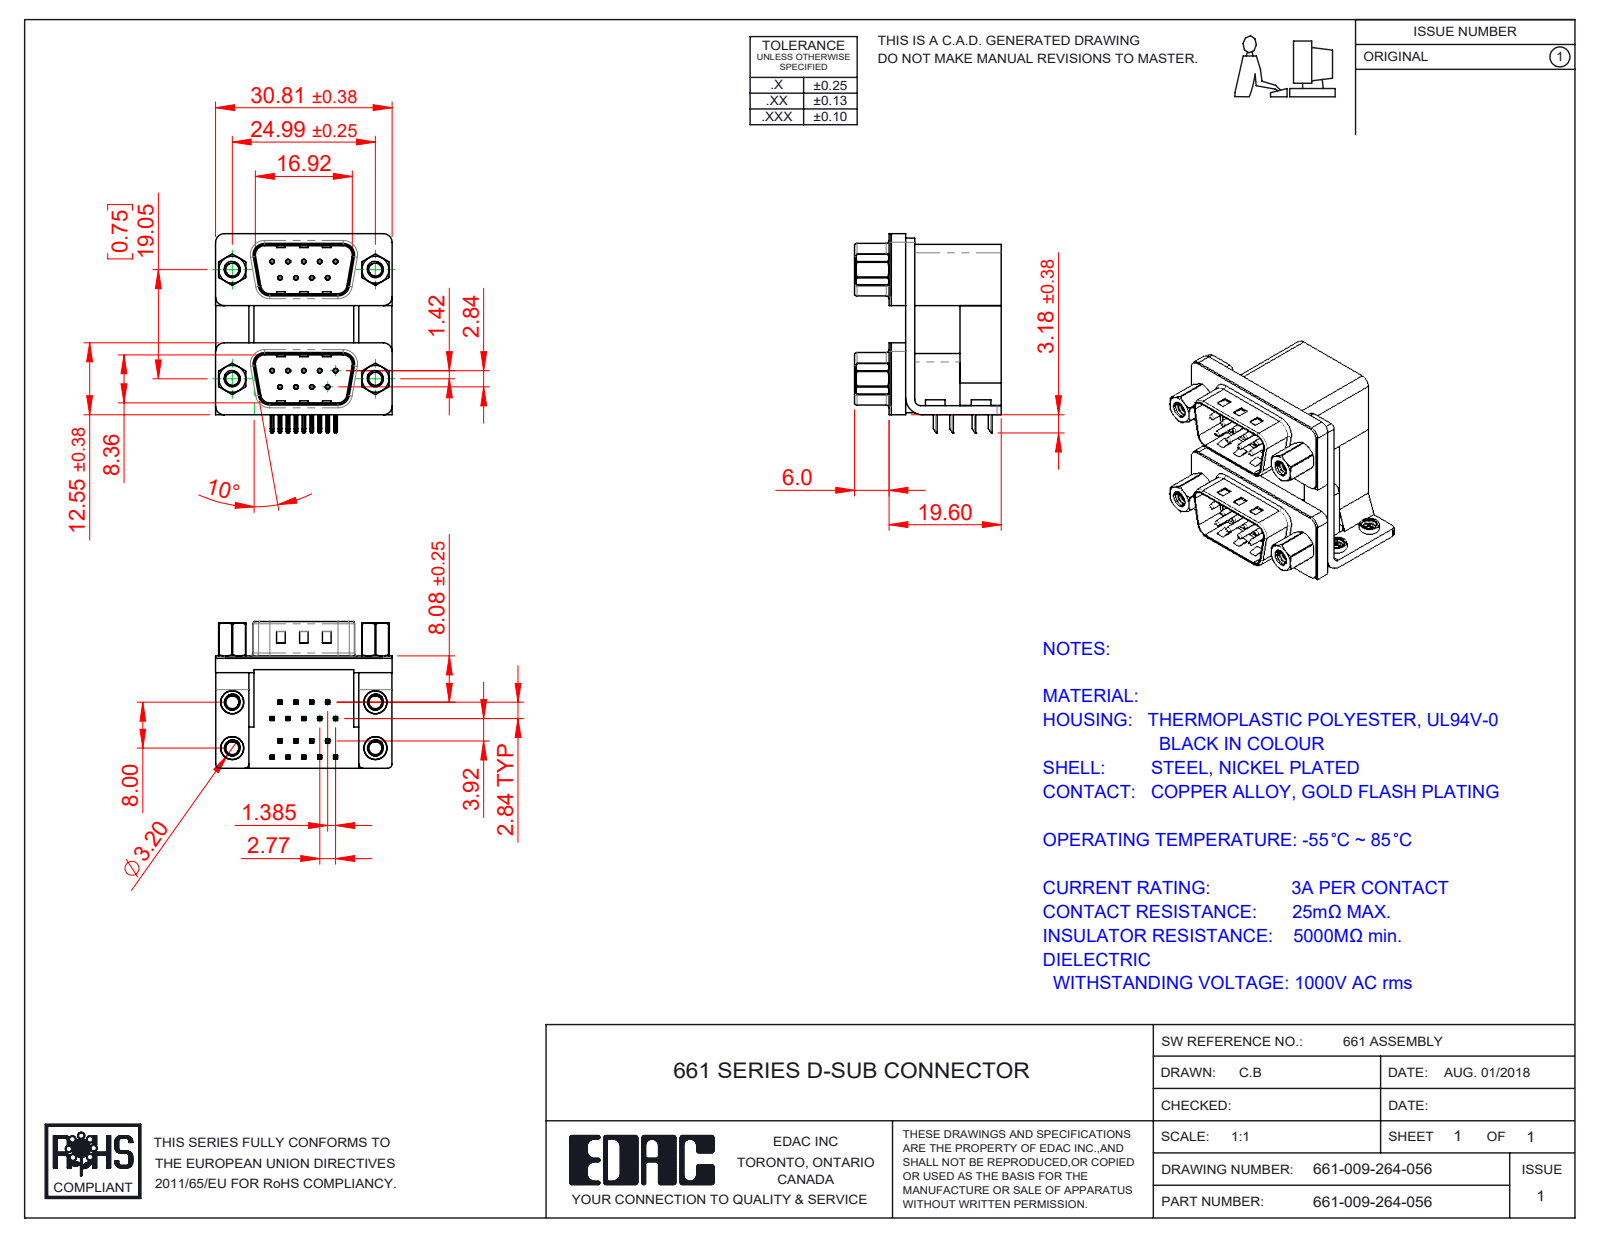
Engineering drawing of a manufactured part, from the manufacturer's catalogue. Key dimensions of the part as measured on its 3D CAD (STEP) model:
Part name (STEP PRODUCT): 661 4-40 Hex Standoff 5; 661 Mounting Bracket_ThruM; 661-009-264-056; 661 Shell_09 Contacts (+8 more)
STEP written by: SolidWorks 2020 (CONFIG_CONTROL_DESIGN)
Units: millimetres
Bodies: 37 solids, 2340 faces (1208 planar, 814 cylindrical, 318 other)
Overall size (bounding box): 34.78 × 30.81 × 25.6
Volume: 10 749 mm³ · Surface area: 13 044 mm²
Round holes (diameter × count): ⌀0.35 ×18, ⌀0.8 ×18, ⌀2.26 ×8, ⌀2.29 ×4, ⌀2.75 ×4, ⌀3.2 ×4, ⌀3.5 ×4, ⌀4 ×4, ⌀4.8 ×4, ⌀5 ×4
Round bosses / shafts (diameter × count): ⌀0.75 ×18, ⌀4.9 ×4, ⌀4.75 ×4, ⌀4 ×4, ⌀3.9 ×4, ⌀3.4 ×4, ⌀2.79 ×4
Partial cylindrical surfaces — rounded edges, fillets, slot ends (radius × count): R0.25 ×72, R0.12 ×36, R0.5 ×16, R1.5 ×14, R0.75 ×8, R0.9 ×8, R1.6 ×8, R2 ×8
Main face-to-face distances: 0.4, 2.5, 19.05, 16.7, 19.2, 10.69, 7.2, 9.5, 12, 1.6
Hole centre spacings: 3.16, 2.77, 19.25, 19.05, 5.54, 19.84, 16.27, 21.93
